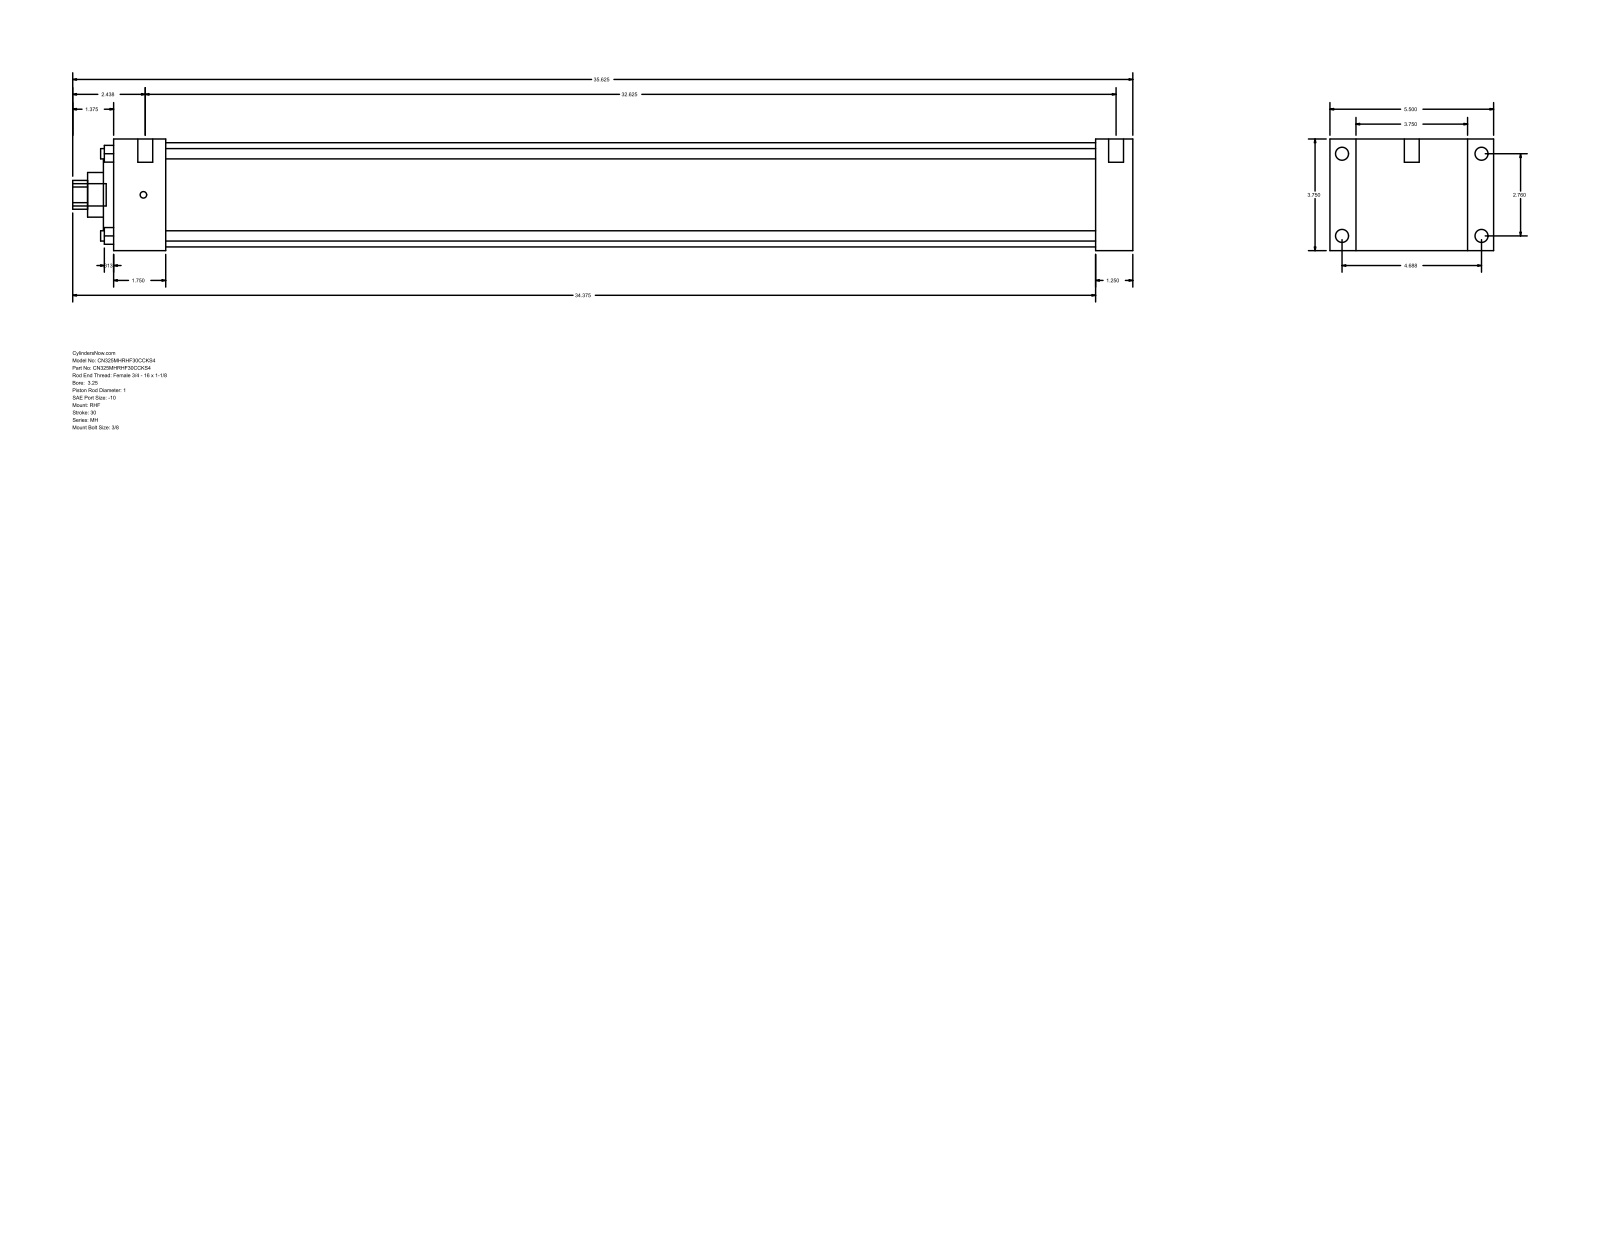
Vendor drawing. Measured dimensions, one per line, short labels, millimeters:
name: MH_RHF__0325_1
written by: GSSL Pune (CONFIG_CONTROL_DESIGN)
unit: mm
bodies: 0 solids, 90 faces (61 planar, 29 cylindrical, 0 other)
size: 904.88 × 139.7 × 95.25
holes: 4× ⌀8.76, 1× ⌀25.4, 1× ⌀38.1, 1× ⌀60.33, 1× ⌀88.9
bosses: 4× ⌀11.13, 4× ⌀5.56, 2× ⌀12.7, 1× ⌀19.05
rounds: 1× R12.29
face distances: 95.24, 31.76, 22.23, 117.47, 838.2, 869.96, 139.7, 44.46, 793.74, 825.5
hole spacings: 49.57, 70.1, 99.14
